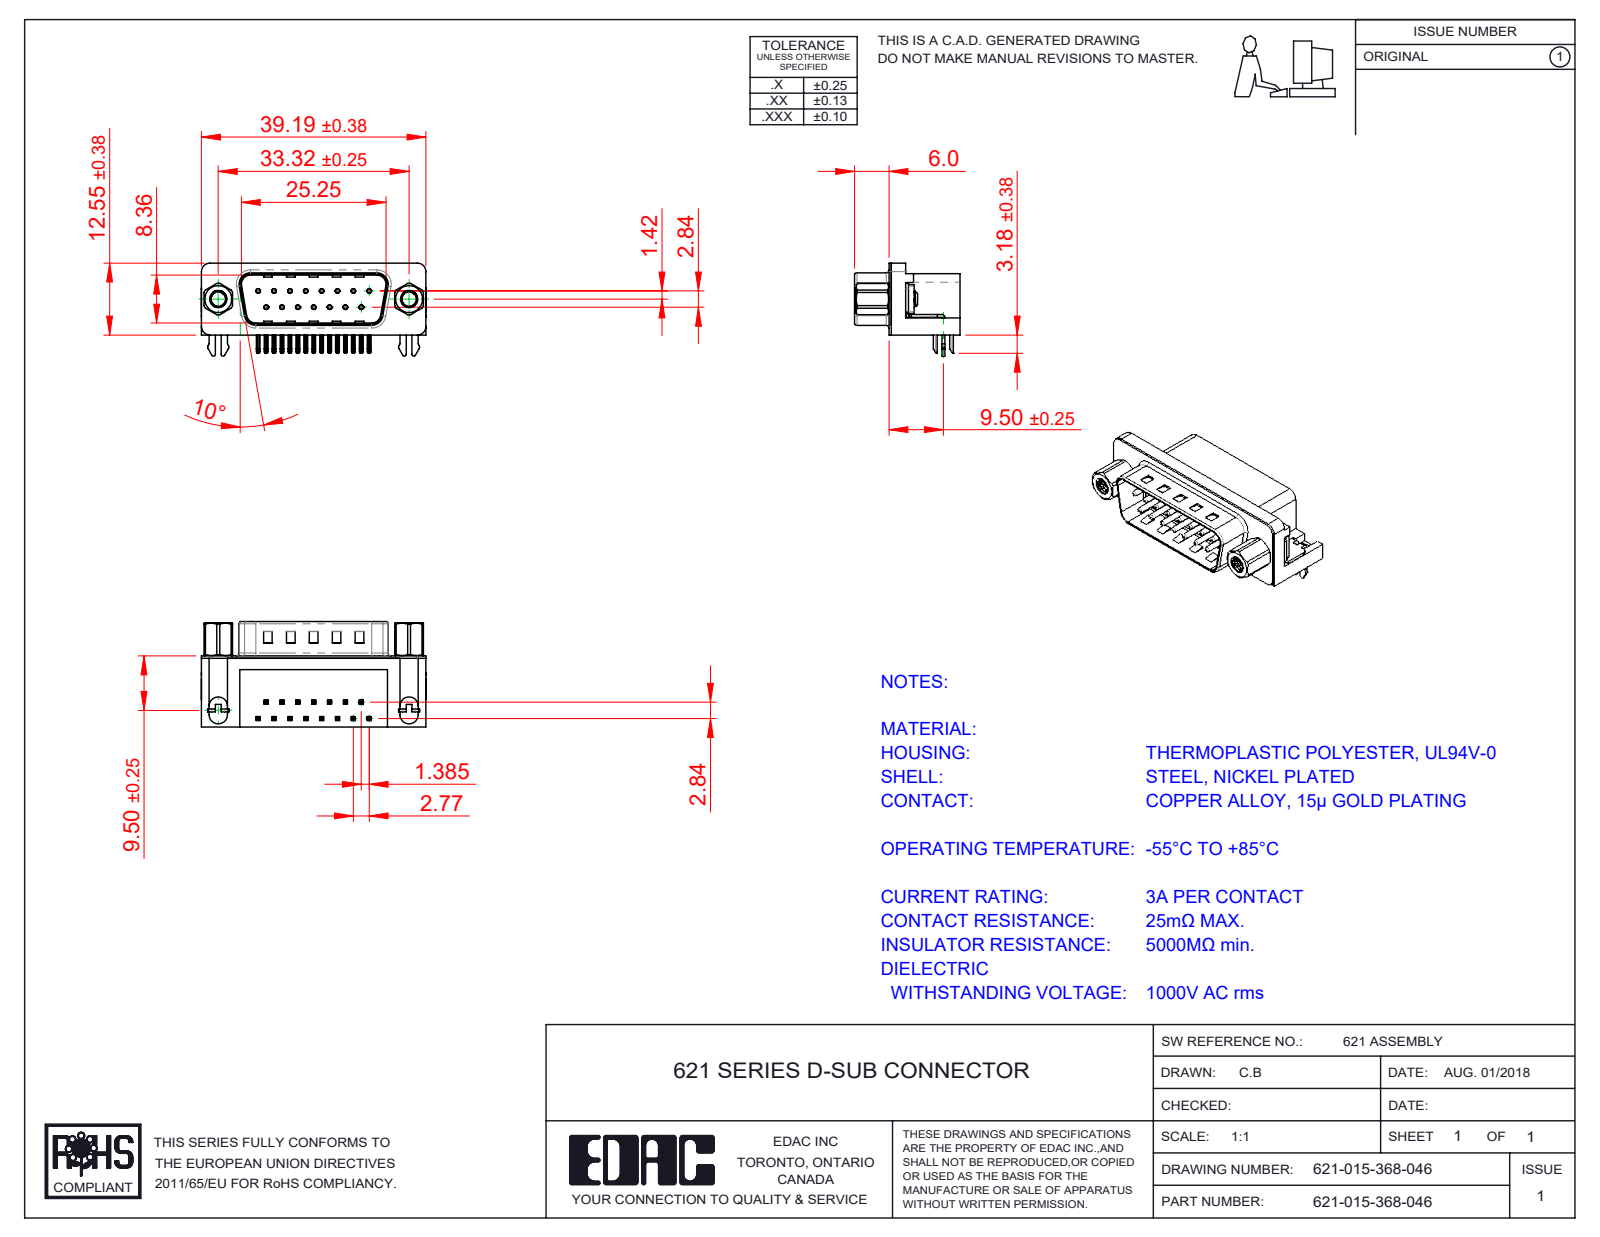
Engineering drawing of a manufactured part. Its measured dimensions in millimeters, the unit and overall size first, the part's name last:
Units: millimetres
Overall size (bounding box): 39.22 × 18.4 × 16.25
Round holes (diameter × count): ⌀0.35 ×15, ⌀0.8 ×15, ⌀2 ×2, ⌀2.5 ×2, ⌀4 ×2, ⌀4.8 ×2, ⌀5 ×2
Round bosses / shafts (diameter × count): ⌀0.75 ×15, ⌀3 ×4, ⌀4.9 ×2, ⌀4.75 ×2, ⌀3.9 ×2
Partial cylindrical surfaces — rounded edges, fillets, slot ends (radius × count): R0.25 ×72, R0.12 ×30, R1 ×16, R0.5 ×9, R1.6 ×8, R1.5 ×6, R0.9 ×4, R2 ×4
Main face-to-face distances: 0.4, 12, 10.35, 12.4, 2.1, 10.46, 1.7, 10.86, 8.76, 9.5
Hole centre spacings: 3.16, 2.77, 5.54, 8.31, 11.08, 5.03, 5.04, 7.48
Volume: 4 664 mm³ · Surface area: 6 257 mm²
Bodies: 23 solids, 1745 faces (957 planar, 547 cylindrical, 241 other)
Part name (STEP PRODUCT): 621 M3 Hex Standoff 5; 621 Contact Bottom; 621 4 Prong Board Lock; 621 Shell_15 Socket (+4 more)
STEP written by: SolidWorks 2016 (CONFIG_CONTROL_DESIGN)
